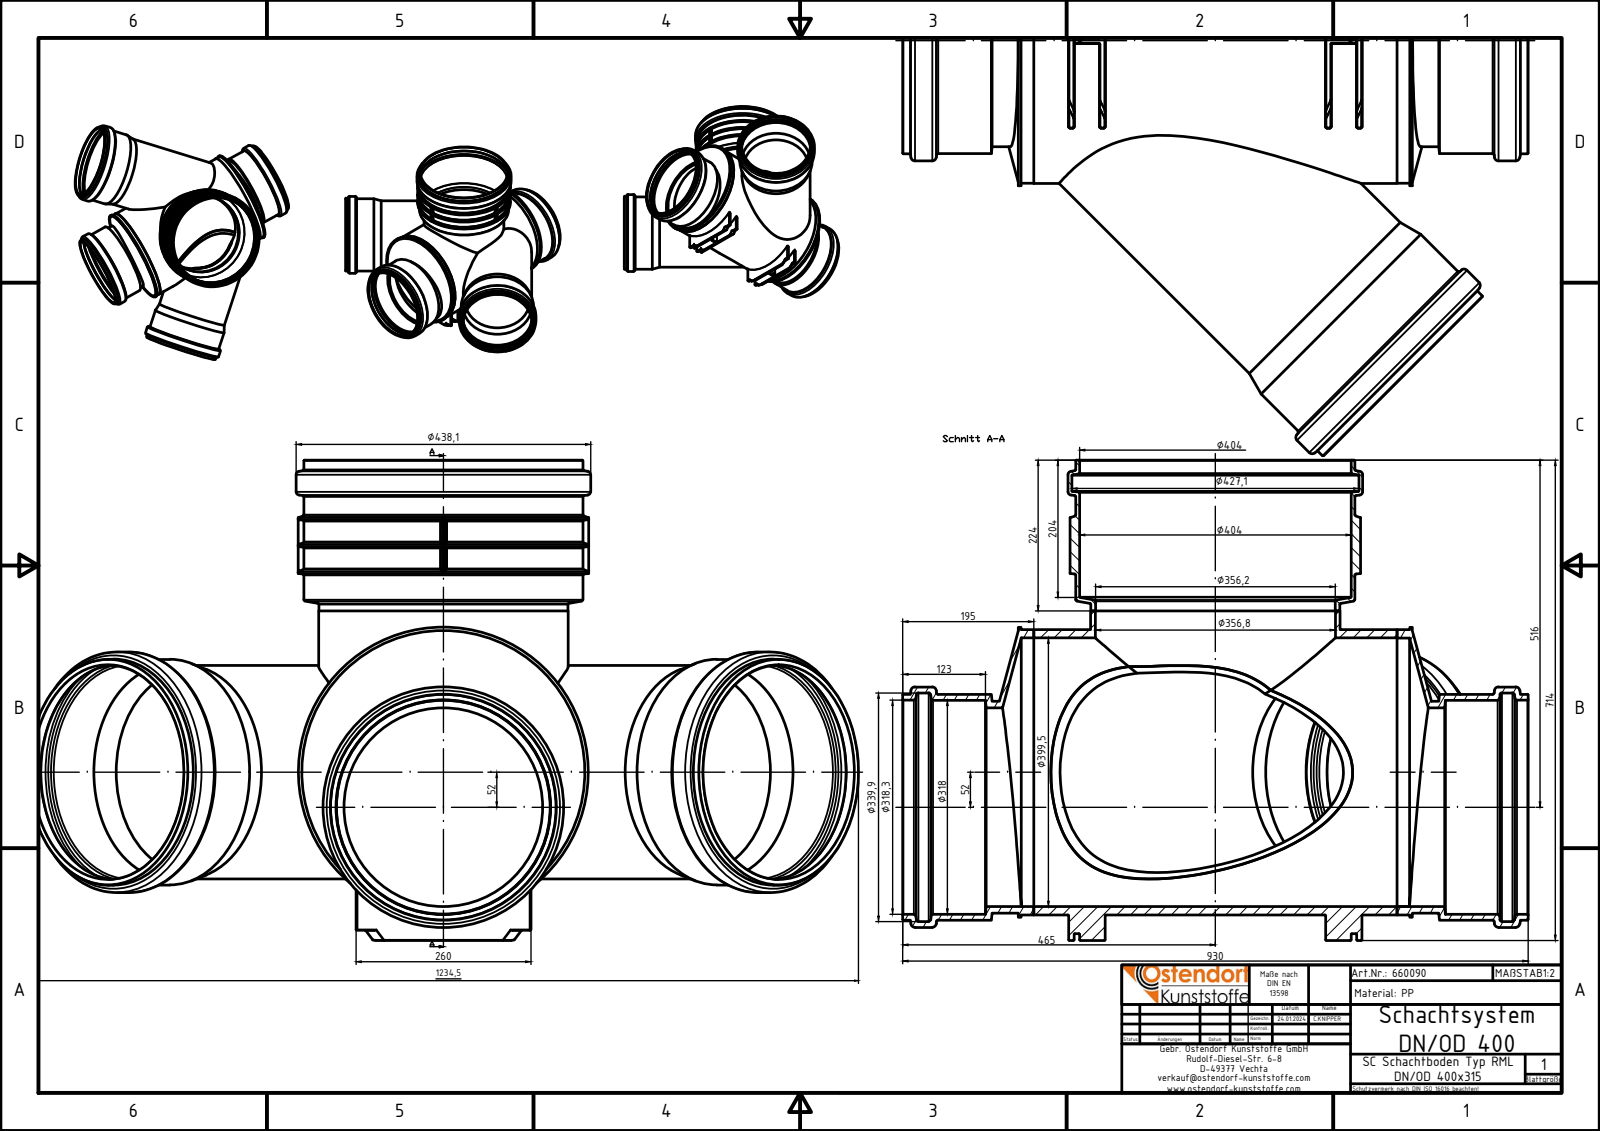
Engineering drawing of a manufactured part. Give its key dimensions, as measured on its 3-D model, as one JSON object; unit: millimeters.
{"part_name": "660090z; 660090 Teil 2; 660090 Teil 1; 660090 Teil 4 (+2 more)", "step_written_by": "Autodesk Inventor 2024 (AUTOMOTIVE_DESIGN)", "units": "millimeters", "bodies": {"solids": 6, "faces": 502, "planar": 87, "cylindrical": 177, "other": 238}, "overall_size": [1234.42, 930, 714], "volume_mm3": 21440000, "surface_area_mm2": 4932000, "round_holes": [[318, 3], [318.3, 3], [339.9, 3], [298, 2], [317.4, 2], [295.5, 1], [356.2, 1], [356.8, 1], [399.4, 1], [399.5, 1], [404, 1], [427.1, 1]], "round_bosses_or_shafts": [[357.5, 3], [335.9, 3], [335.6, 3], [317.4, 2], [438.1, 1], [432, 1], [431, 1], [424.1, 1]], "partial_cylinders_radius": [[1, 52], [2, 24], [4, 2]], "face_to_face_distances": [8, 46, 382, 540, 434, 106, 480, 60, 374, 52], "hole_center_spacings": [52]}
